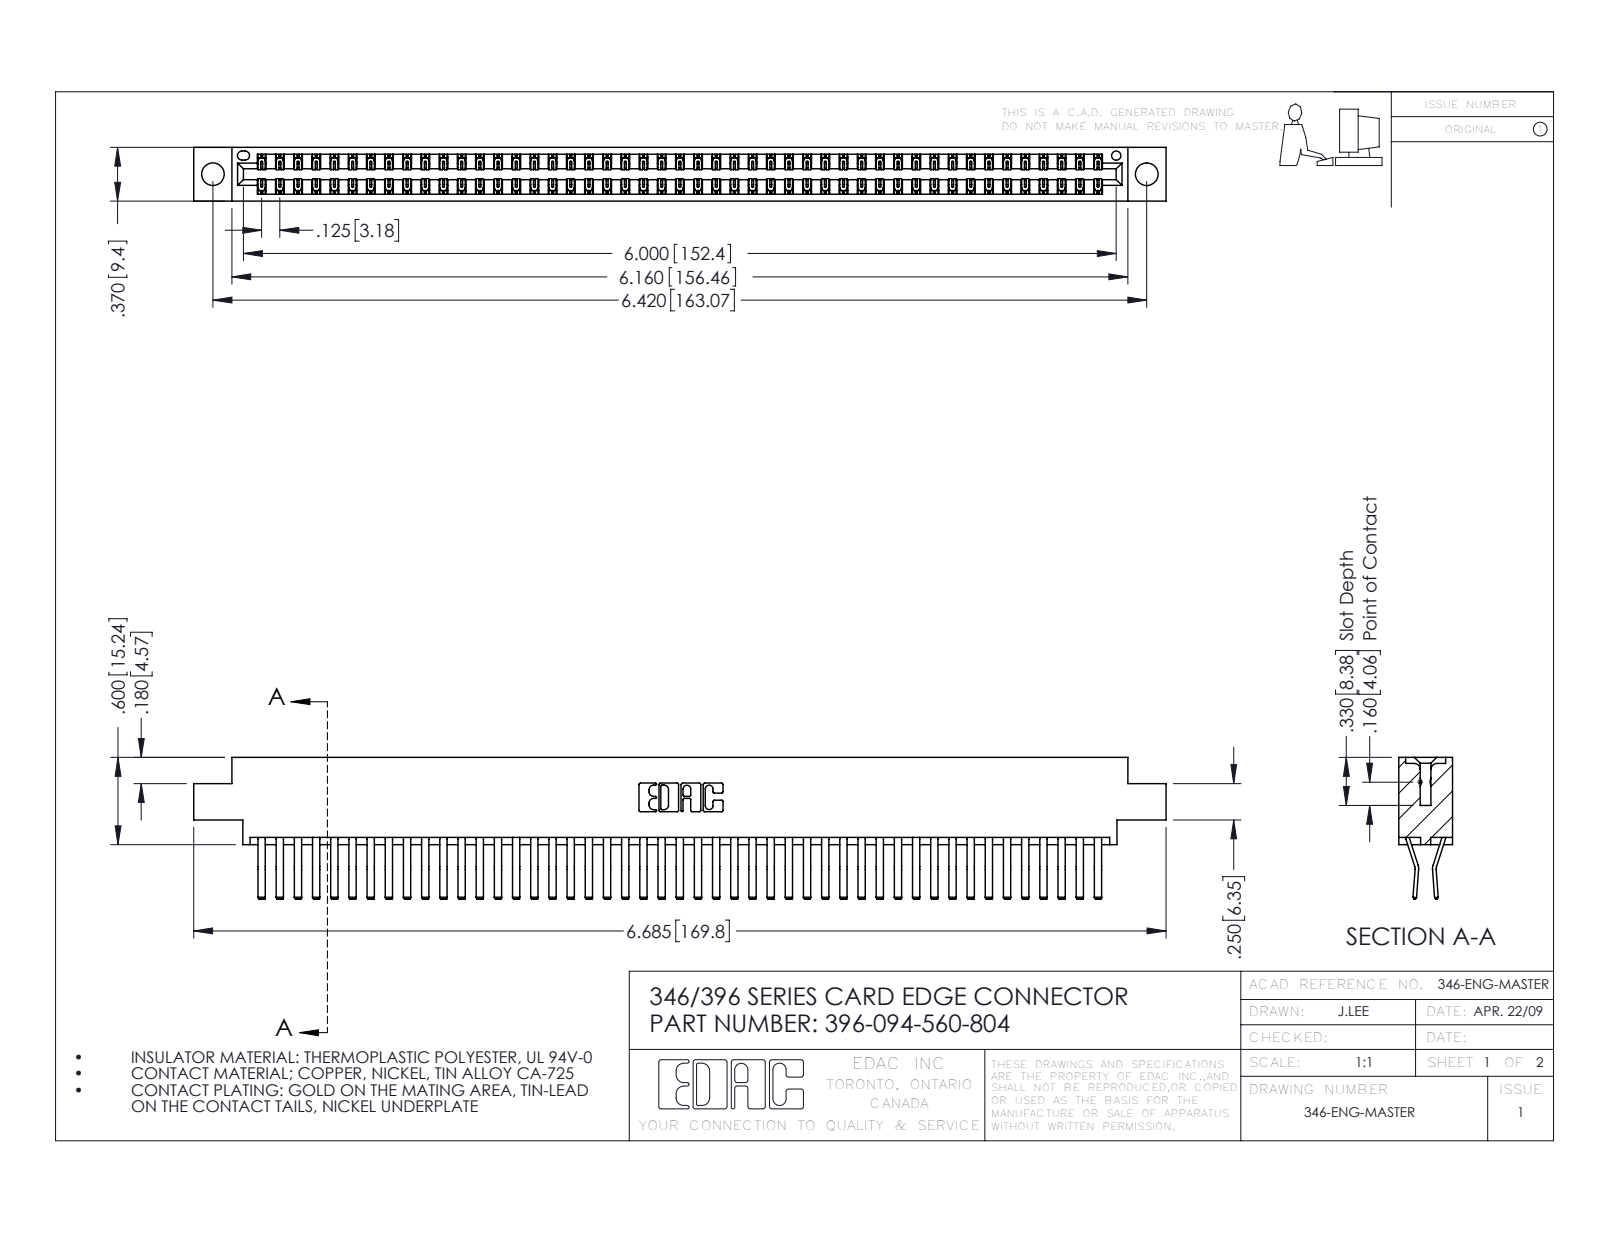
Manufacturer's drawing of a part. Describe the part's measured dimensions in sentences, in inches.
The part is named "345-292-001_560 Tail; 346 Part_0.170 Offset - 0.156 Dia-TH; 396-094-560-804". Its 3-D file was written by "SolidWorks 2016 (CONFIG_CONTROL_DESIGN)". It is 95 solids with 5202 faces: 3370 planar, 1832 cylindrical and 0 other. Overall it measures 6.685 by 0.975 by 0.37 inches. Its volume is 1.036 cubic inches and its surface area 38.81 square inches. Round holes: 2 of diameter 0.156, 1 of diameter 0.064. Partial cylindrical surfaces (rounded edges, fillets, slot ends): 141 of radius 0.006, 22 of radius 0.01, 6 of radius 0.007, 6 of radius 0.031, 3 of radius 0.026, 2 of radius 0.01, 2 of radius 0.014, 2 of radius 0.022. The main face-to-face distances are 0.048, 0.322, 0.37, 0.025, 0.25, 0.072, 0.298, 0.275, 0.148, 0.222. The hole center spacings are 0.246, 6.211, 6.42.
